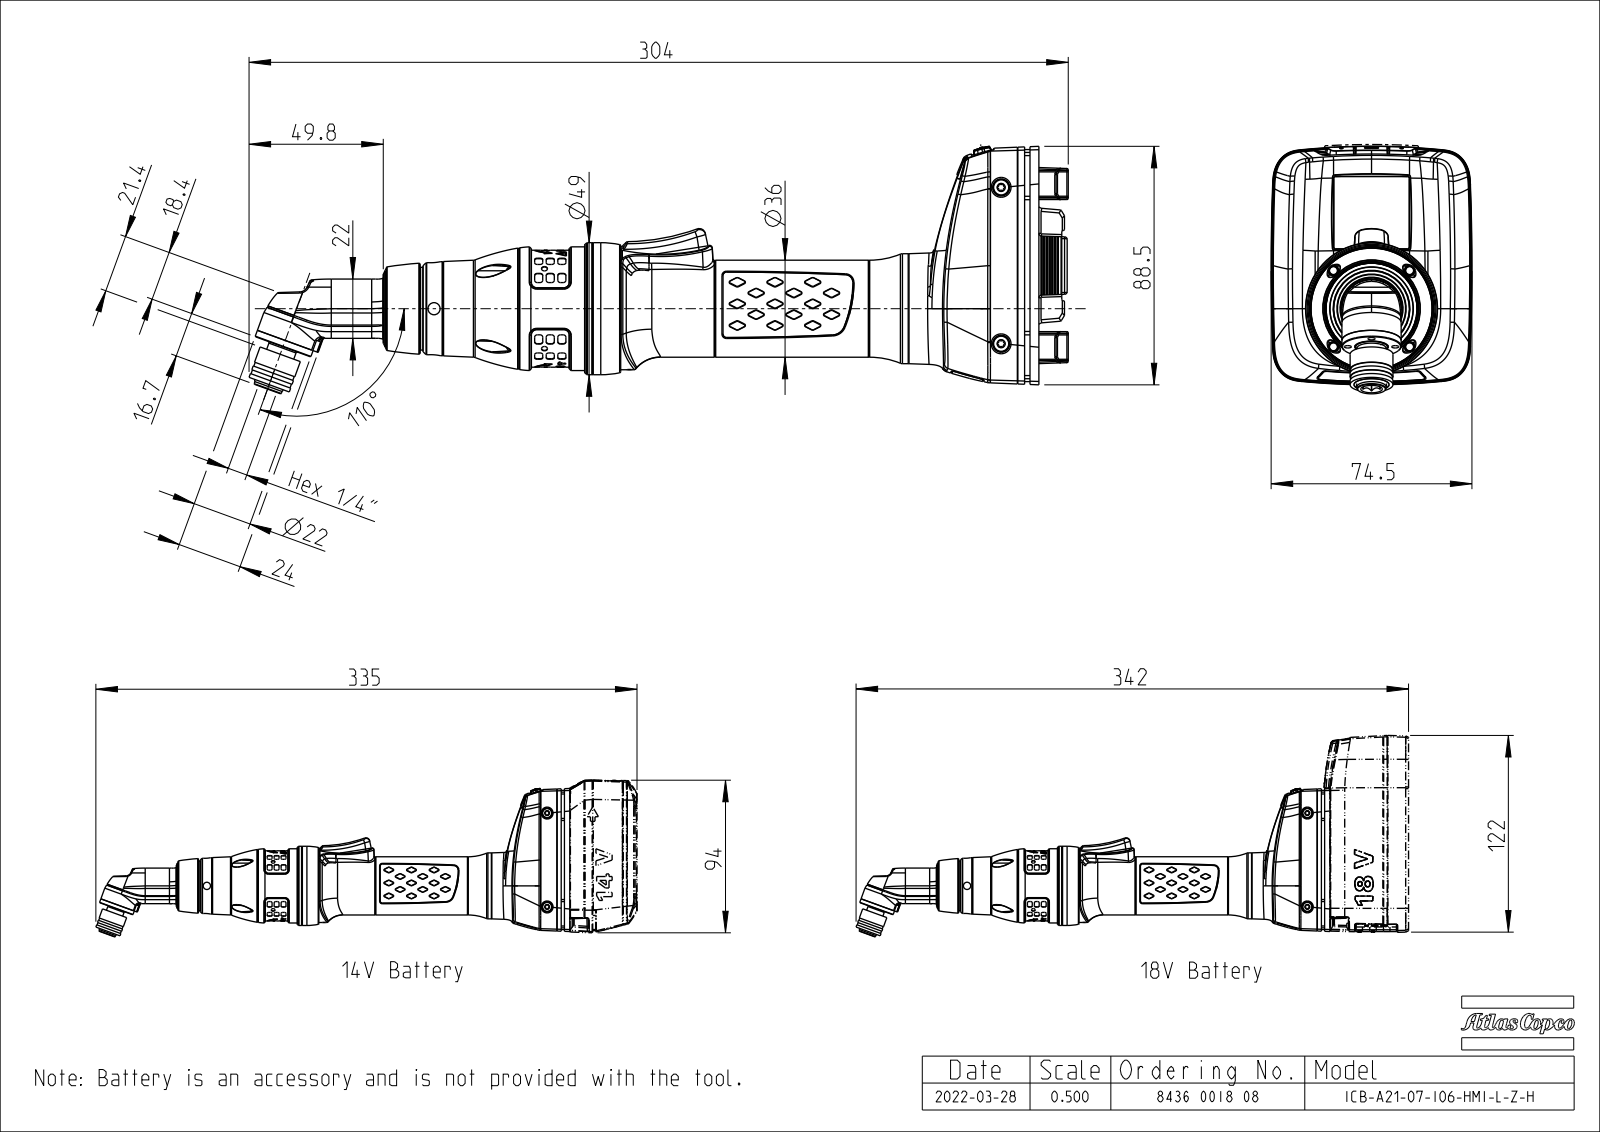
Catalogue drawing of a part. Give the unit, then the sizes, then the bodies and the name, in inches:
Units: inches
Overall size (bounding box): 11.974 × 3.616 × 2.935
Round holes (diameter × count): ⌀0.102 ×4, ⌀0.177 ×2, ⌀0.128 ×1, ⌀0.138 ×1, ⌀0.315 ×1, ⌀0.421 ×1, ⌀0.472 ×1, ⌀0.492 ×1, ⌀0.551 ×1, ⌀0.565 ×1, ⌀1.685 ×1, ⌀1.72 ×1
Round bosses / shafts (diameter × count): ⌀0.315 ×4, ⌀0.22 ×3, ⌀1.929 ×1, ⌀1.807 ×1, ⌀1.783 ×1, ⌀1.713 ×1, ⌀1.709 ×1, ⌀1.689 ×1
Partial cylindrical surfaces — rounded edges, fillets, slot ends (radius × count): R0.039 ×77, R0.02 ×72, R0.006 ×34, R0.008 ×33, R0.011 ×30, R0.02 ×30, R0.012 ×24, R0.015 ×24
Main face-to-face distances: 4.744, 4.743, 0.413, 5.156, 5.157, 0.331, 2.362, 0.421, 4.735, 4.736
Hole centre spacings: 0.346, 0.49, 0.693, 9.077
Volume: 28.84 in³ · Surface area: 120.6 in²
Bodies: 2 solids, 3890 faces (984 planar, 783 cylindrical, 2123 other)
Part name (STEP PRODUCT): EXT_COMP_SW0021
STEP written by: CREO PARAMETRIC BY PTC INC, 2020281 (CONFIG_CONTROL_DESIGN)
